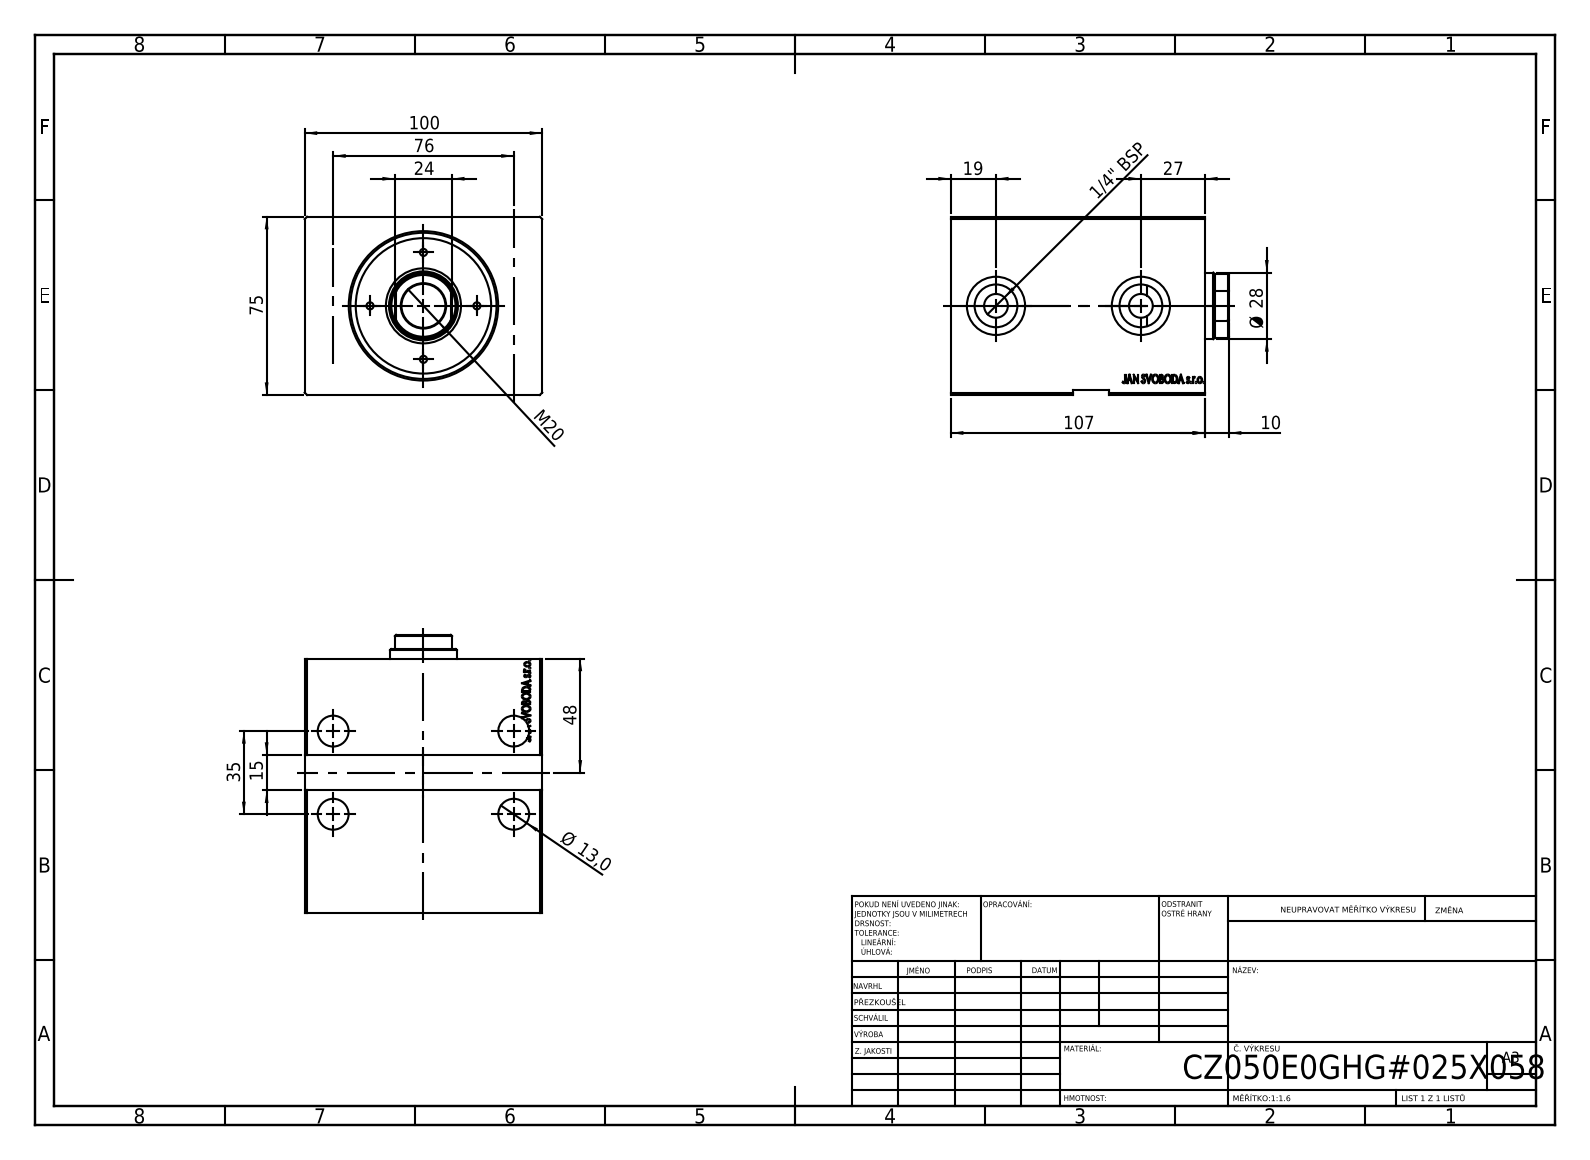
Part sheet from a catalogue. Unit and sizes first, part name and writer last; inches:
Units: inches
Overall size (bounding box): 4.213 × 3.937 × 2.953
Round holes (diameter × count): ⌀0.512 ×4, ⌀0.315 ×2, ⌀0.394 ×2, ⌀0.709 ×2, ⌀0.965 ×2, ⌀1.417 ×1, ⌀1.969 ×1, ⌀2.421 ×1
Main face-to-face distances: 2.953, 3.937, 4.213, 3.512, 0.701, 0.079, 2.874, 4.205, 0.693, 0.394
Hole centre spacings: 1.378, 2.992, 3.294, 0.828, 0.928, 1.371, 1.614, 2.029
Volume: 34.61 in³ · Surface area: 123.2 in²
Bodies: 1 solid, 776 faces (375 planar, 31 cylindrical, 370 other)
STEP written by: SolidWorks 2019 (CONFIG_CONTROL_DESIGN)
